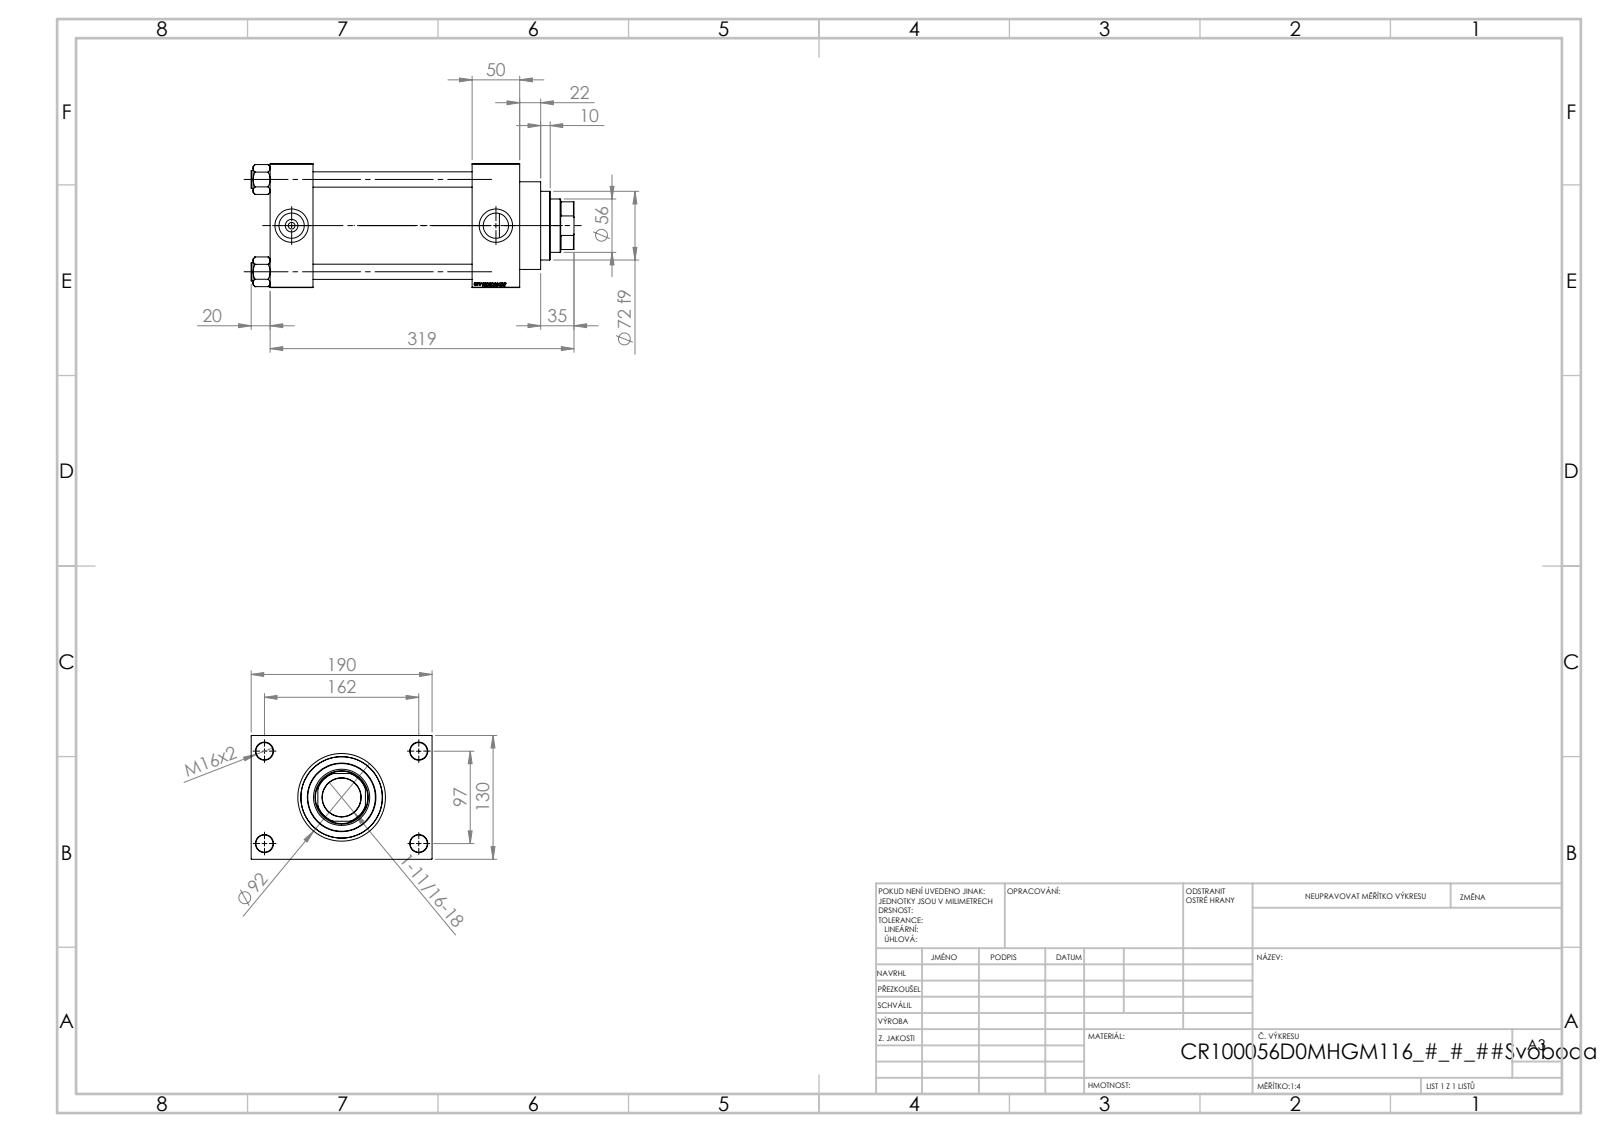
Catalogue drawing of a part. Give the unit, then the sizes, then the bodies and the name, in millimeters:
Units: millimetres
Overall size (bounding box): 339 × 190 × 130
Round holes (diameter × count): ⌀16 ×4, ⌀18 ×4, ⌀7 ×2, ⌀26.44 ×2, ⌀35 ×2, ⌀40.5 ×1, ⌀56 ×1, ⌀59 ×1, ⌀76 ×1, ⌀85.5 ×1, ⌀100 ×1
Round bosses / shafts (diameter × count): ⌀19 ×4, ⌀106 ×1, ⌀92 ×1, ⌀72 ×1
Partial cylindrical surfaces — rounded edges, fillets, slot ends (radius × count): R27 ×1
Main face-to-face distances: 130, 50, 45, 212, 167, 262, 217, 30, 160, 116
Hole centre spacings: 32.55, 68.52, 94.41, 96.9, 102.27, 129.45, 161.73, 97
Volume: 3 035 000 mm³ · Surface area: 460 682 mm²
Bodies: 11 solids, 1151 faces (545 planar, 88 cylindrical, 518 other)
Part name (STEP PRODUCT): V215CR_D_Body; NUT_M5_D; V215CR_VCP_D; V215CR_D_TYCINKA (+1 more)
STEP written by: SolidWorks 2019 (CONFIG_CONTROL_DESIGN)
